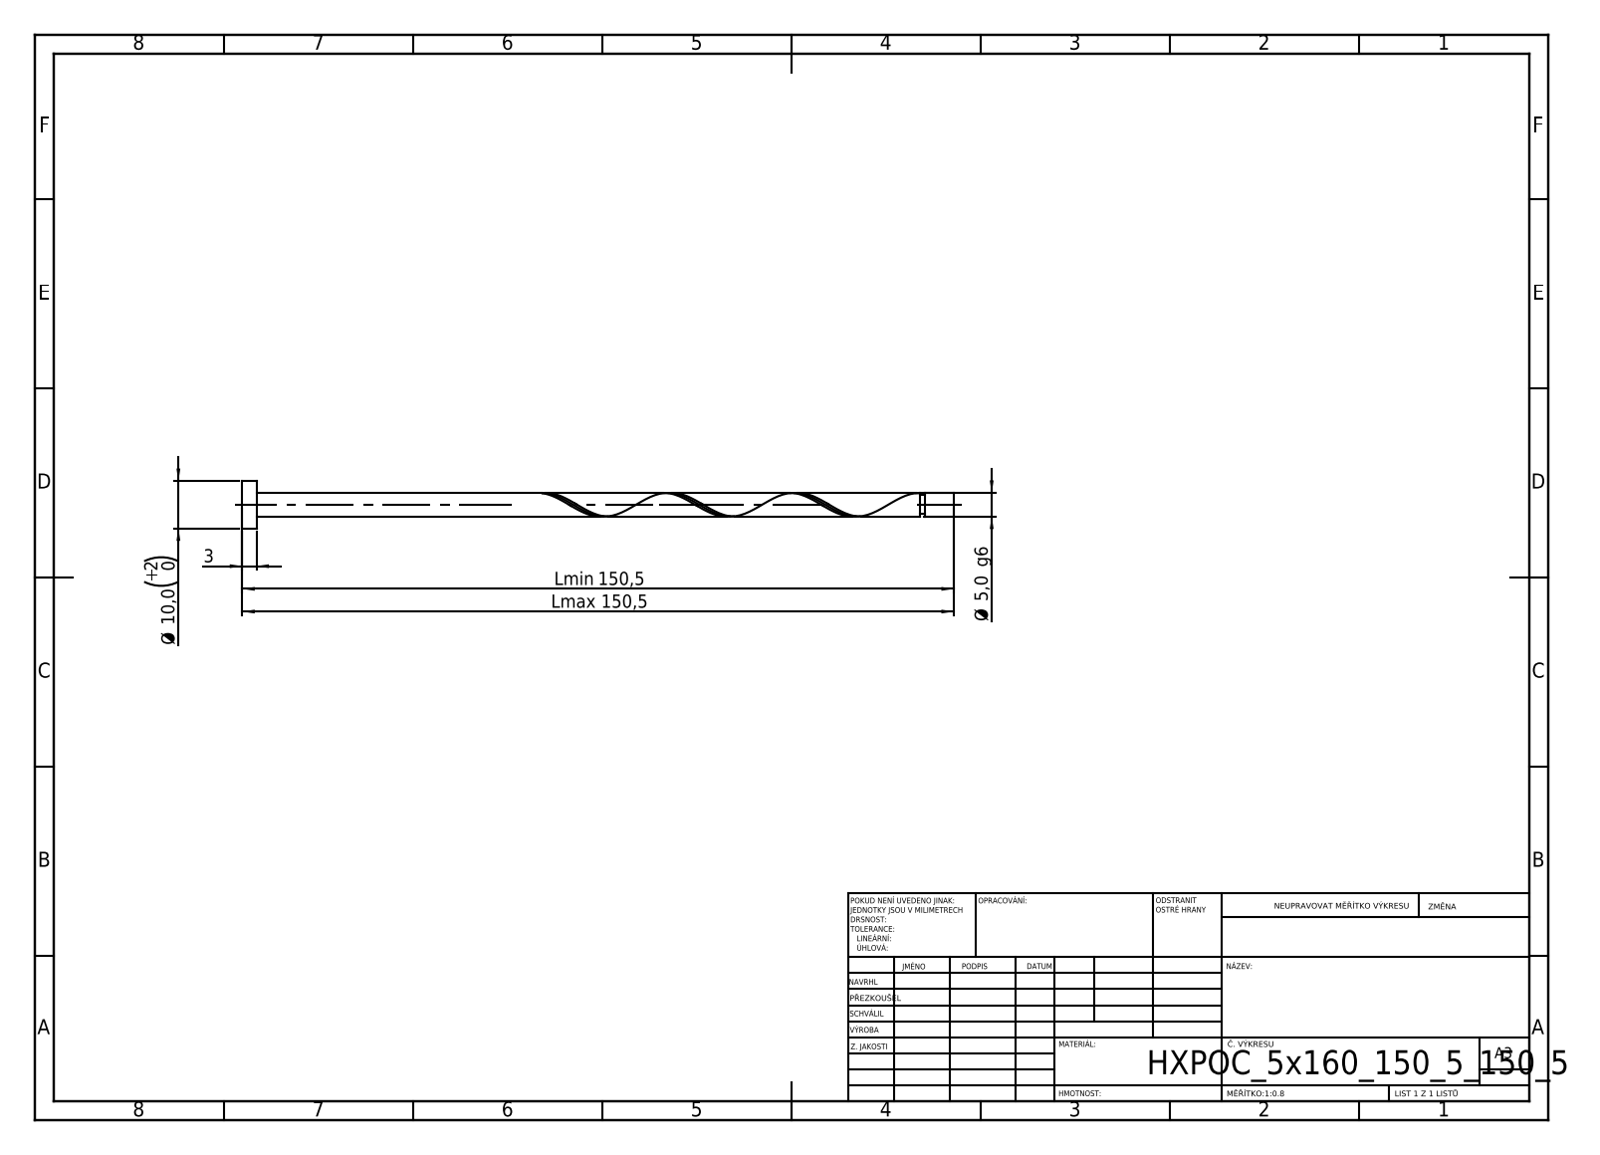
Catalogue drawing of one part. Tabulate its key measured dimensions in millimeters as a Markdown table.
| quantity | value |
| --- | --- |
| STEP written by | SolidWorks 2019 (CONFIG_CONTROL_DESIGN) |
| units | millimeters |
| bodies | 1 solid, 21 faces (6 planar, 14 cylindrical, 1 other) |
| overall size | 150.5 × 10 × 10 |
| volume | 3 095 mm³ |
| surface area | 2 626 mm² |
| round bosses / shafts (diameter × count) | 10 × 1, 5 × 1, 4 × 1 |
| main face-to-face distances | 3, 150.5, 147.5, 144.29, 141.29, 6.21, 143.29, 140.29, 1, 7.21 |
